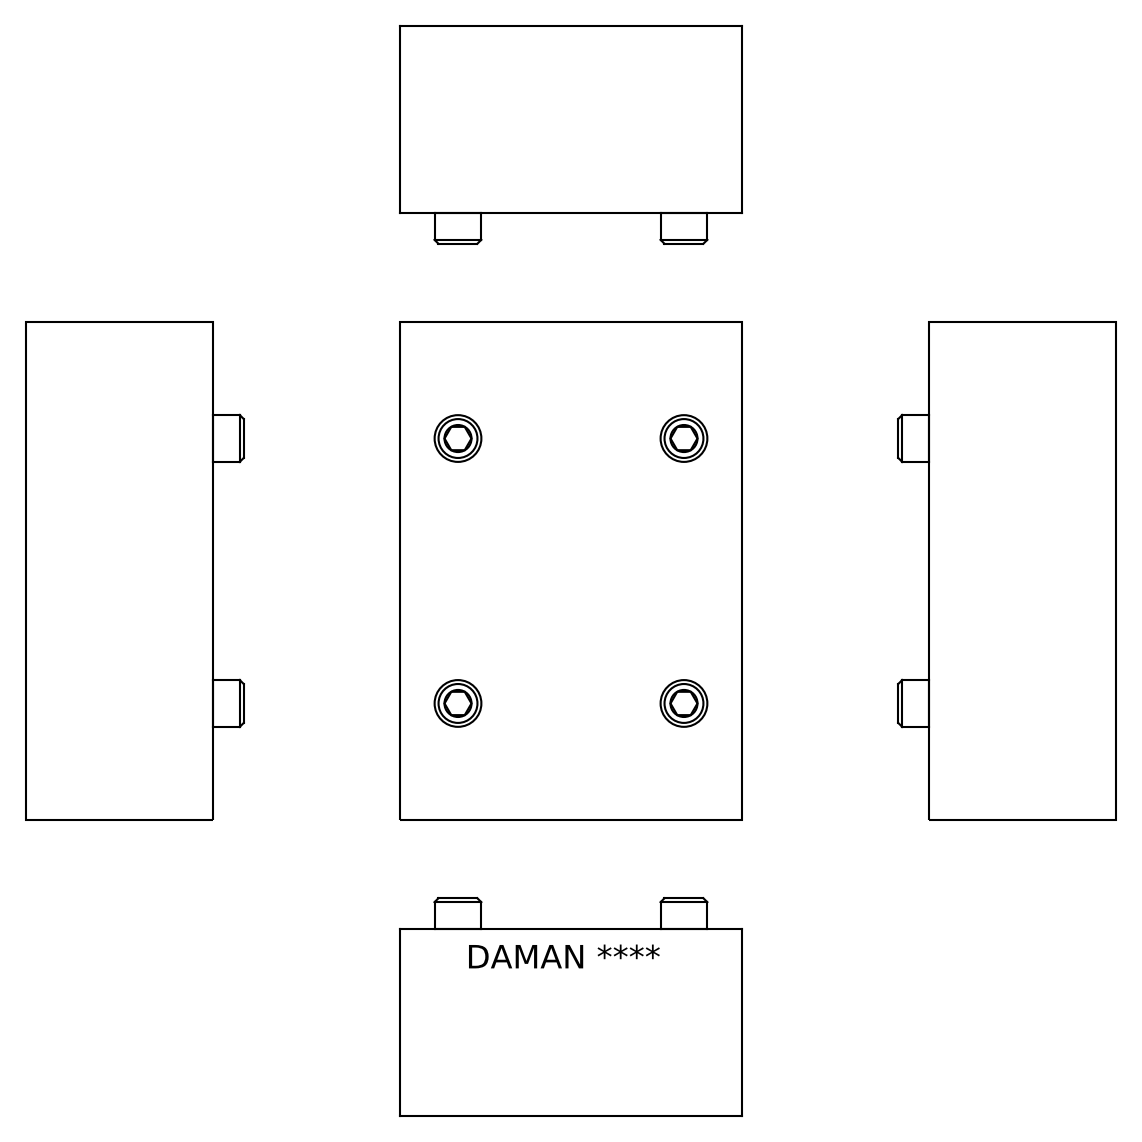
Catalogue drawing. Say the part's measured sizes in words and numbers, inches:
The part is named "D05HCOP". Its 3-D file was written by "Autodesk Inventor 2020 (AUTOMOTIVE_DESIGN)". It is 1 solid with 326 faces: 221 planar, 25 cylindrical and 80 other. Overall it measures 4 by 2.75 by 1.5 inches. Its volume is 15.54 cubic inches and its surface area 50.54 square inches. Round holes: 4 of diameter 0.281, 2 of diameter 0.438, 2 of diameter 0.625. Partial cylindrical surfaces (rounded edges, fillets, slot ends): 3 of radius 0.219, 3 of radius 0.313, 2 of radius 0.756, 1 of radius 0.187, 1 of radius 0.219, 1 of radius 0.305, 1 of radius 0.309, 1 of radius 0.313. The main face-to-face distances are 1.5, 2.75, 4, 0.052, 1.448, 0.5, 0.448, 1, 0.04, 0.46. The hole center spacings are 2.793, 0.448, 0.537, 0.546, 0.713, 0.951, 1.287, 1.288.
